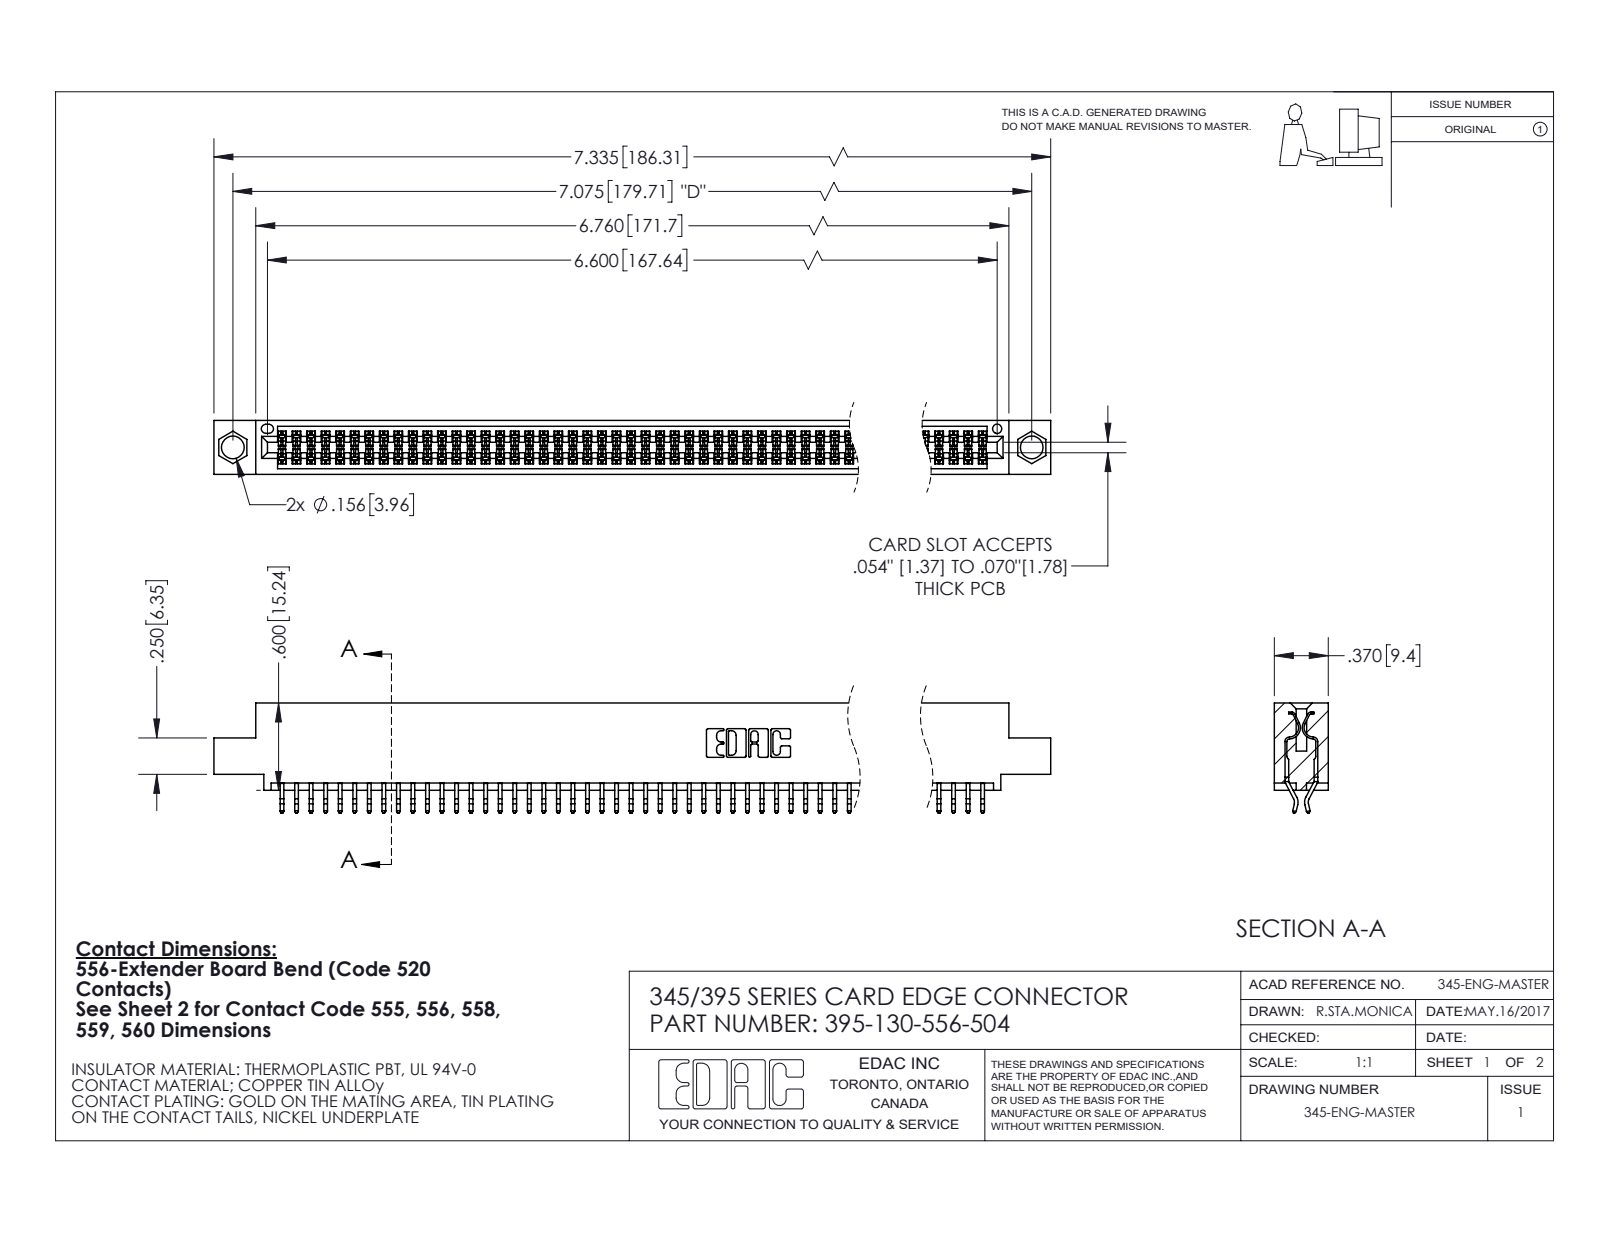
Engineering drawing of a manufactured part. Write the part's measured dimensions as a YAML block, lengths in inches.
part_name: "345 Part_0.110 Offset - 0.156 Dia-TI; 395-130-556-504; 345-292-001_556 Tail"
step_written_by: "SolidWorks 2020 (CONFIG_CONTROL_DESIGN)"
units: inches
bodies: {solids: 131, faces: 7424, planar: 4908, cylindrical: 2516, other: 0}
overall_size: [7.335, 0.757, 0.37]
volume: 1.106
surface_area: 41.96
round_holes:
  - {diameter: 0.156, count: 2}
  - {diameter: 0.064, count: 1}
partial_cylinders:
  - {radius: 0.006, count: 260}
  - {radius: 0.01, count: 22}
  - {radius: 0.007, count: 6}
  - {radius: 0.031, count: 6}
  - {radius: 0.026, count: 3}
  - {radius: 0.01, count: 2}
  - {radius: 0.014, count: 2}
  - {radius: 0.019, count: 2}
face_to_face_distances: [0.298, 0.072, 0.37, 0.2, 0.025, 0.098, 0.272, 0.225, 0.175, 0.149]
hole_center_spacings: [0.27, 6.839, 7.075]
